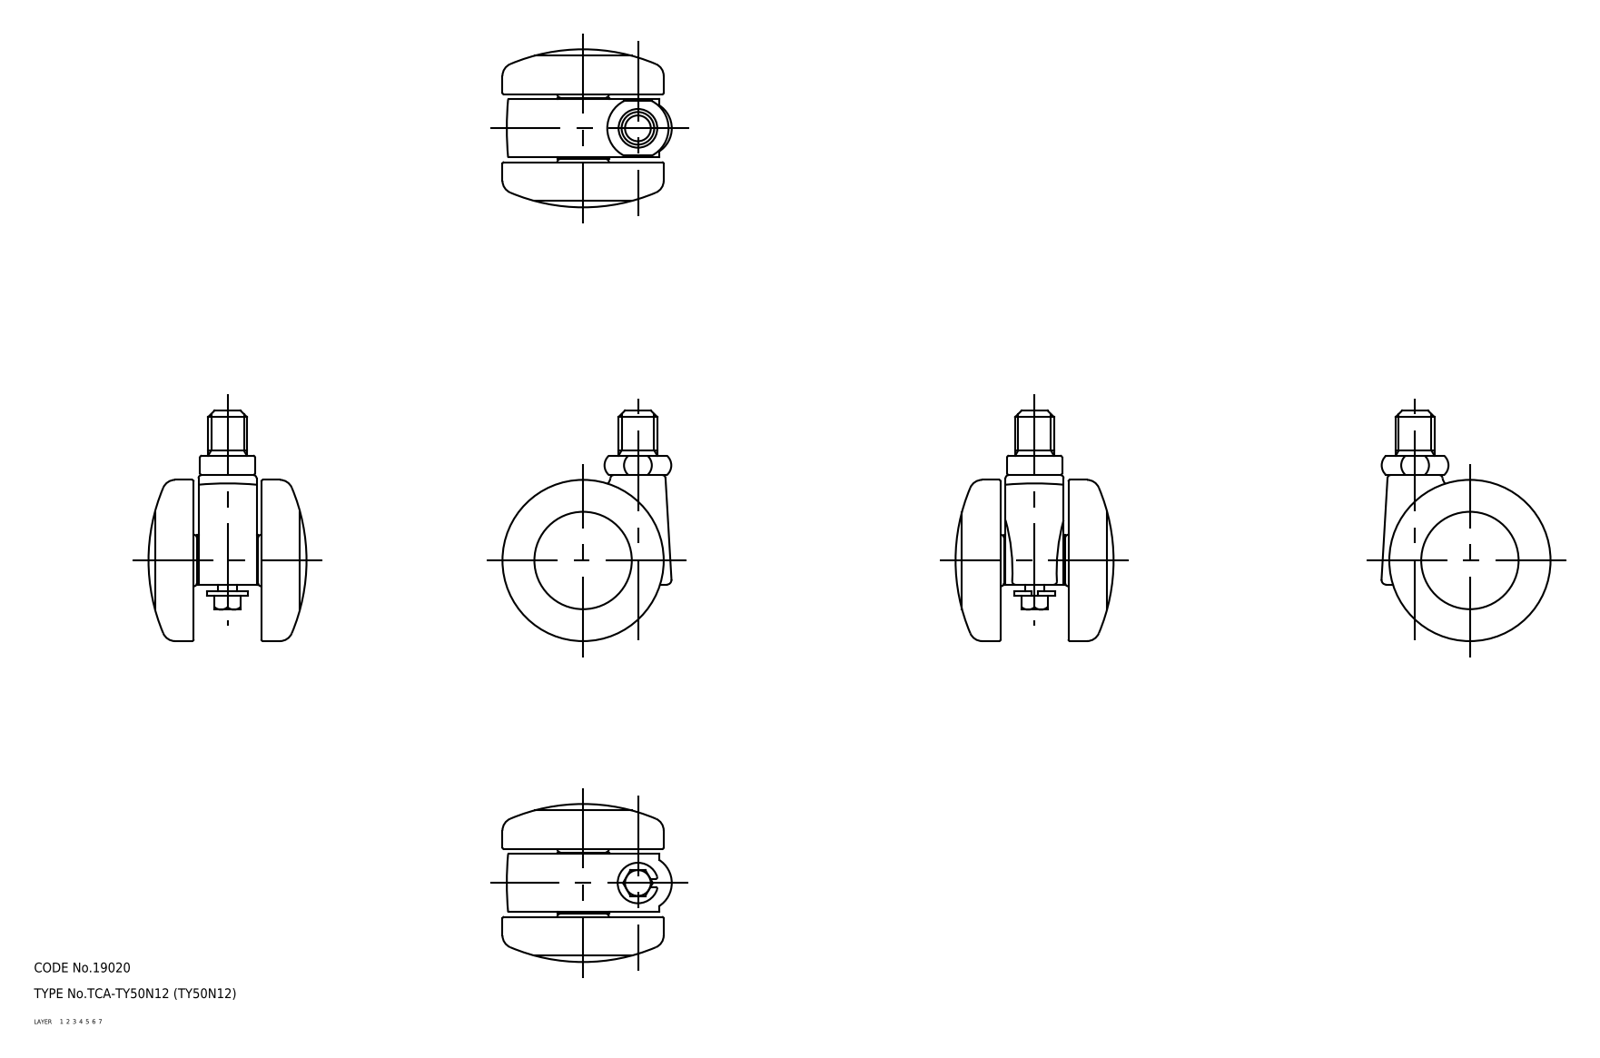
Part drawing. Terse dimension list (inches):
name: wheel; main shaft; TY50N12_10975_36
written by: CADfix (AUTOMOTIVE_DESIGN)
unit: in
bodies: 4 solids, 124 faces (0 planar, 0 cylindrical, 124 other)
size: 2.815 × 2.064 × 1.929
volume: 3.922 in³; area: 39.58 in²
